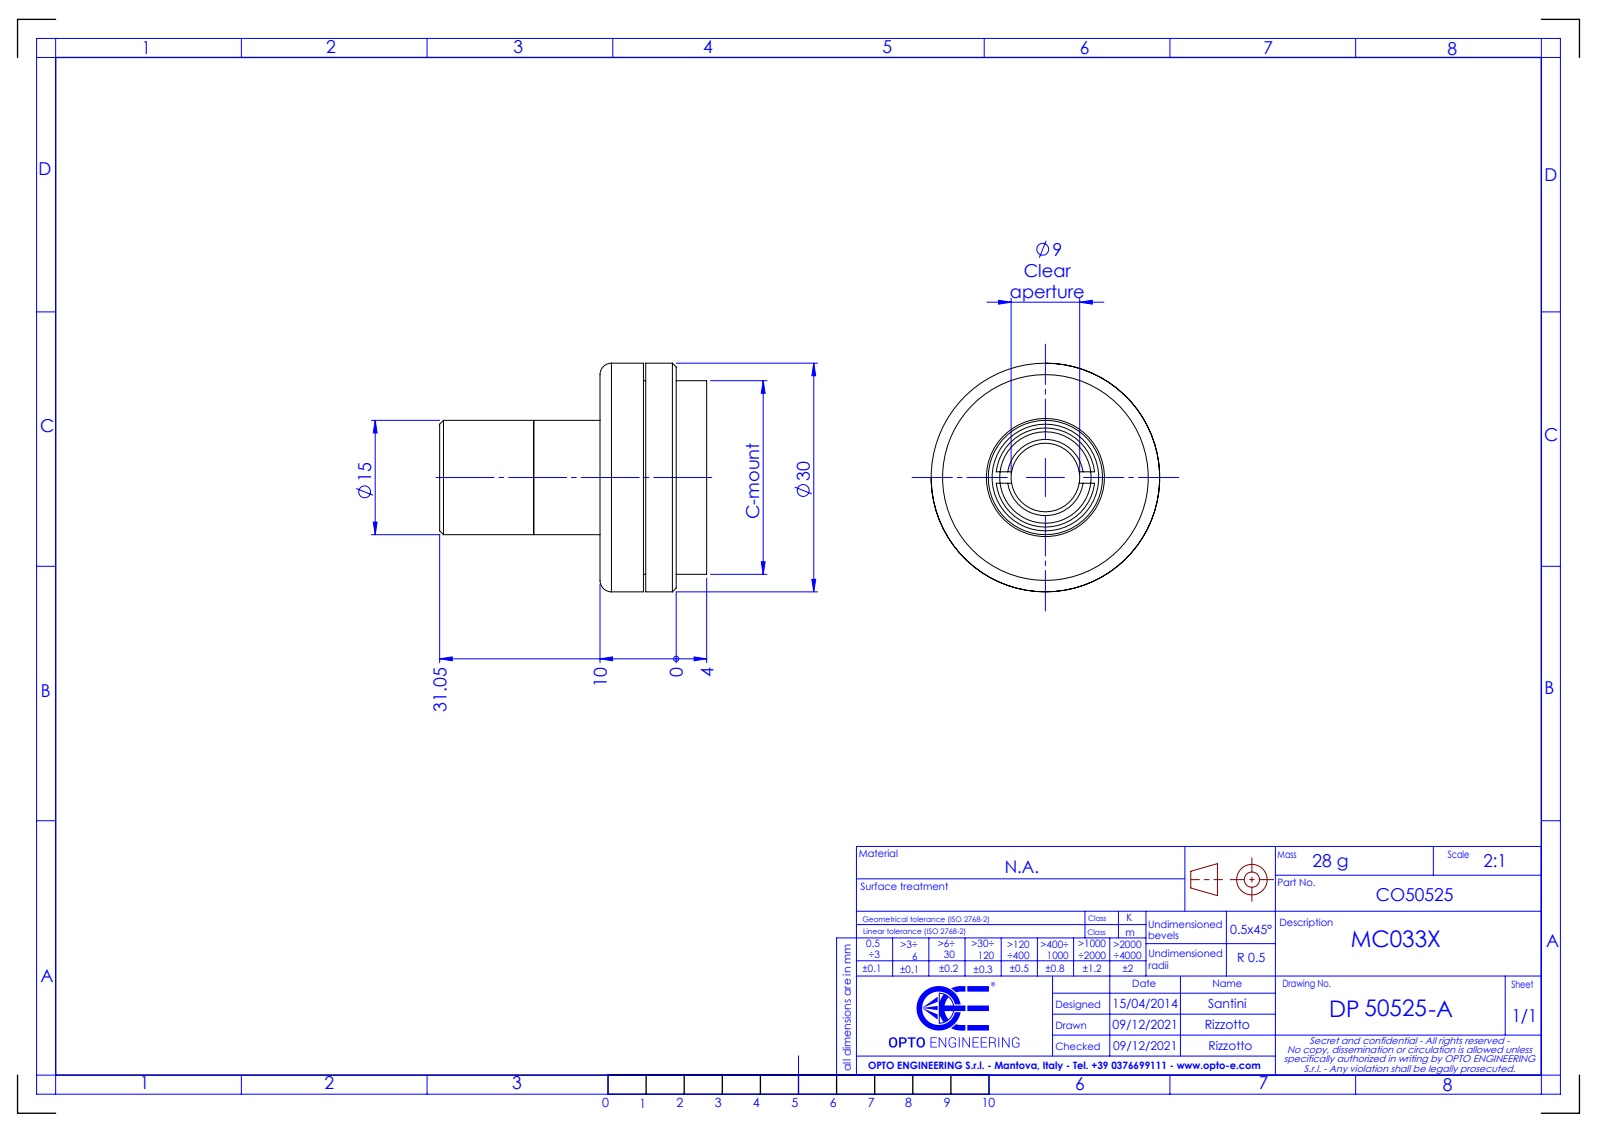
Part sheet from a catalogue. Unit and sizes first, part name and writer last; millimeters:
Units: millimetres
Overall size (bounding box): 35.05 × 30 × 30
Round holes (diameter × count): ⌀9 ×1, ⌀12 ×1
Round bosses / shafts (diameter × count): ⌀30 ×1, ⌀25.4 ×1, ⌀15 ×1, ⌀14.5 ×1
Main face-to-face distances: 4, 6, 5.7, 10, 4.3, 14, 8.3, 8, 21.05, 26.75
Bodies: 0 solids, 47 faces (14 planar, 18 cylindrical, 15 other)
Part name (STEP PRODUCT): DP50525-A_MC033X
STEP written by: SolidWorks 2021 (CONFIG_CONTROL_DESIGN)
